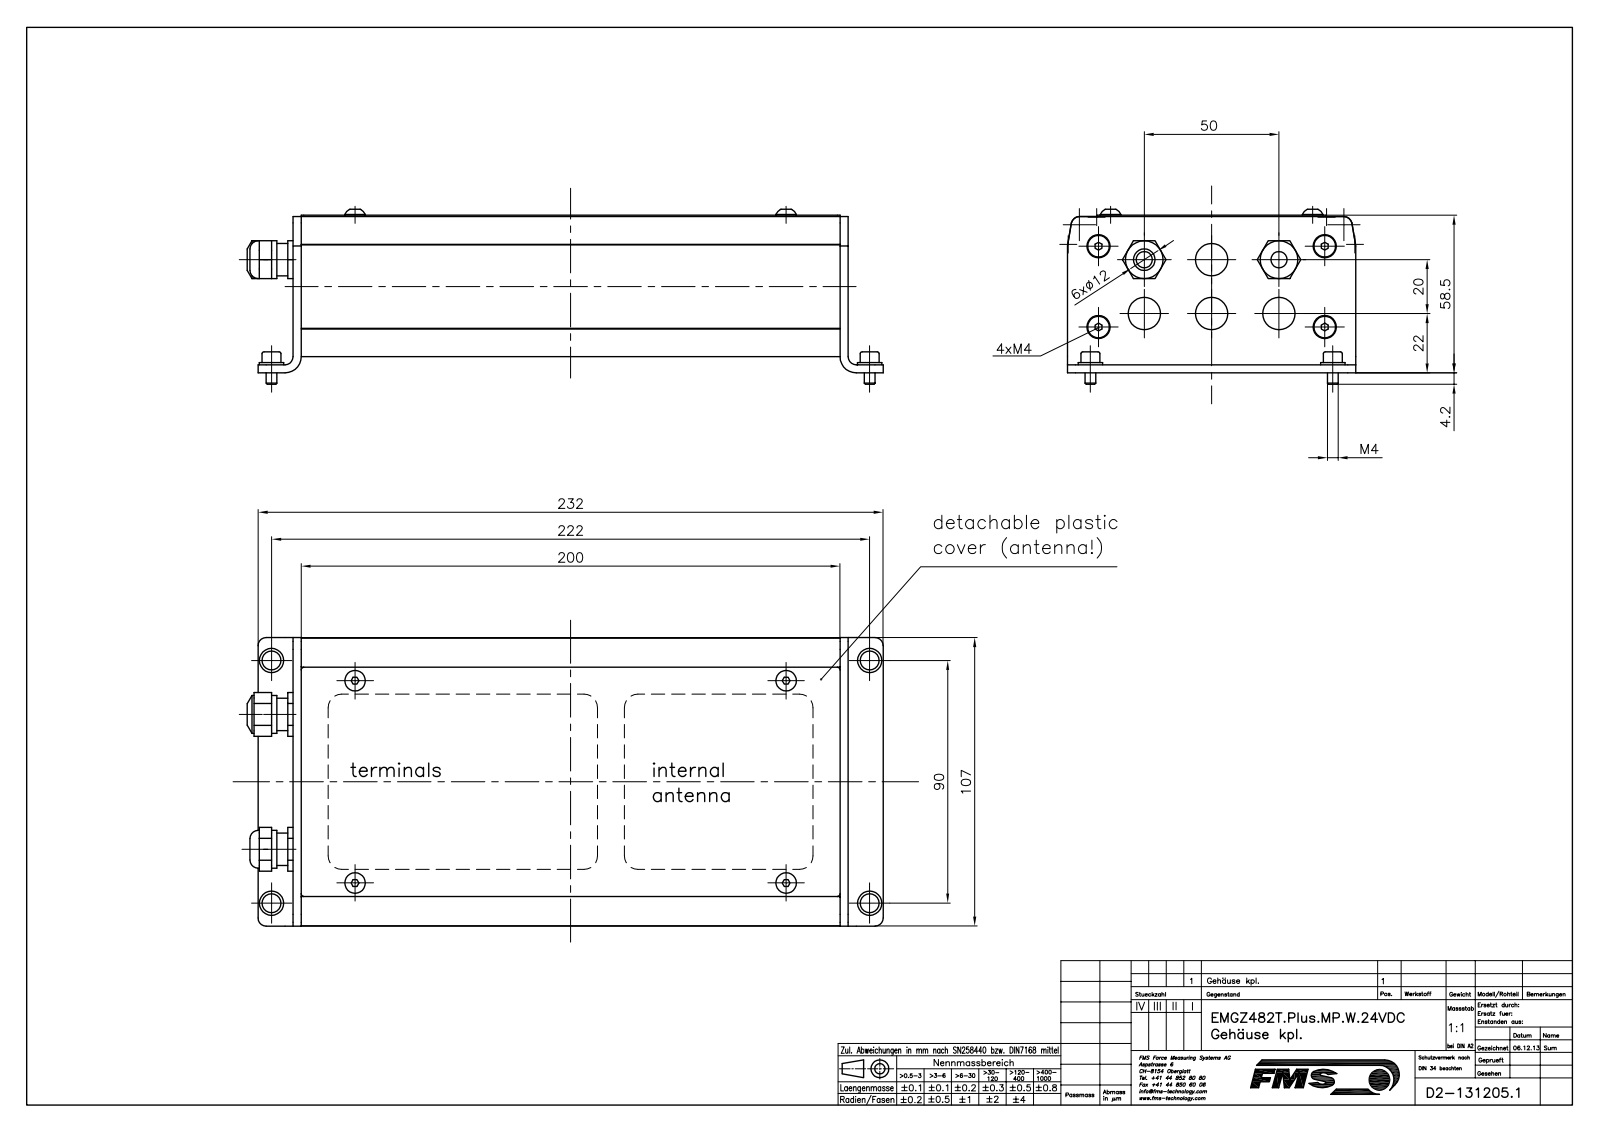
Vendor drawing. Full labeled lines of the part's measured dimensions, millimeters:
Part name (STEP PRODUCT): T1312051; T1312052; T1312053; T1312054 (+8 more)
STEP written by: Mechanical Desktop 2009 (CONFIG_CONTROL_DESIGN)
Units: millimetres
Bodies: 36 solids, 948 faces (488 planar, 324 cylindrical, 136 other)
Overall size (bounding box): 266.3 × 210.2 × 107
Volume: 226 913 mm³ · Surface area: 223 180 mm²
Round holes (diameter × count): ⌀3.42 ×12, ⌀4.3 ×12, ⌀4.8 ×4, ⌀12 ×4, ⌀6 ×2
Round bosses / shafts (diameter × count): ⌀4 ×16, ⌀8 ×8, ⌀9 ×4, ⌀7.6 ×4, ⌀7 ×4, ⌀14 ×2, ⌀12 ×2
Partial cylindrical surfaces — rounded edges, fillets, slot ends (radius × count): R2 ×20, R3 ×10, R0.2 ×8, R2.15 ×8, R5 ×8, R4 ×6, R1 ×4, R1.5 ×4
Main face-to-face distances: 2, 49, 47, 51, 3, 4, 3.5, 1.5, 45, 2.5
Hole centre spacings: 10, 17.72, 22.3, 25, 30.23, 31.89, 32.02, 42.3
